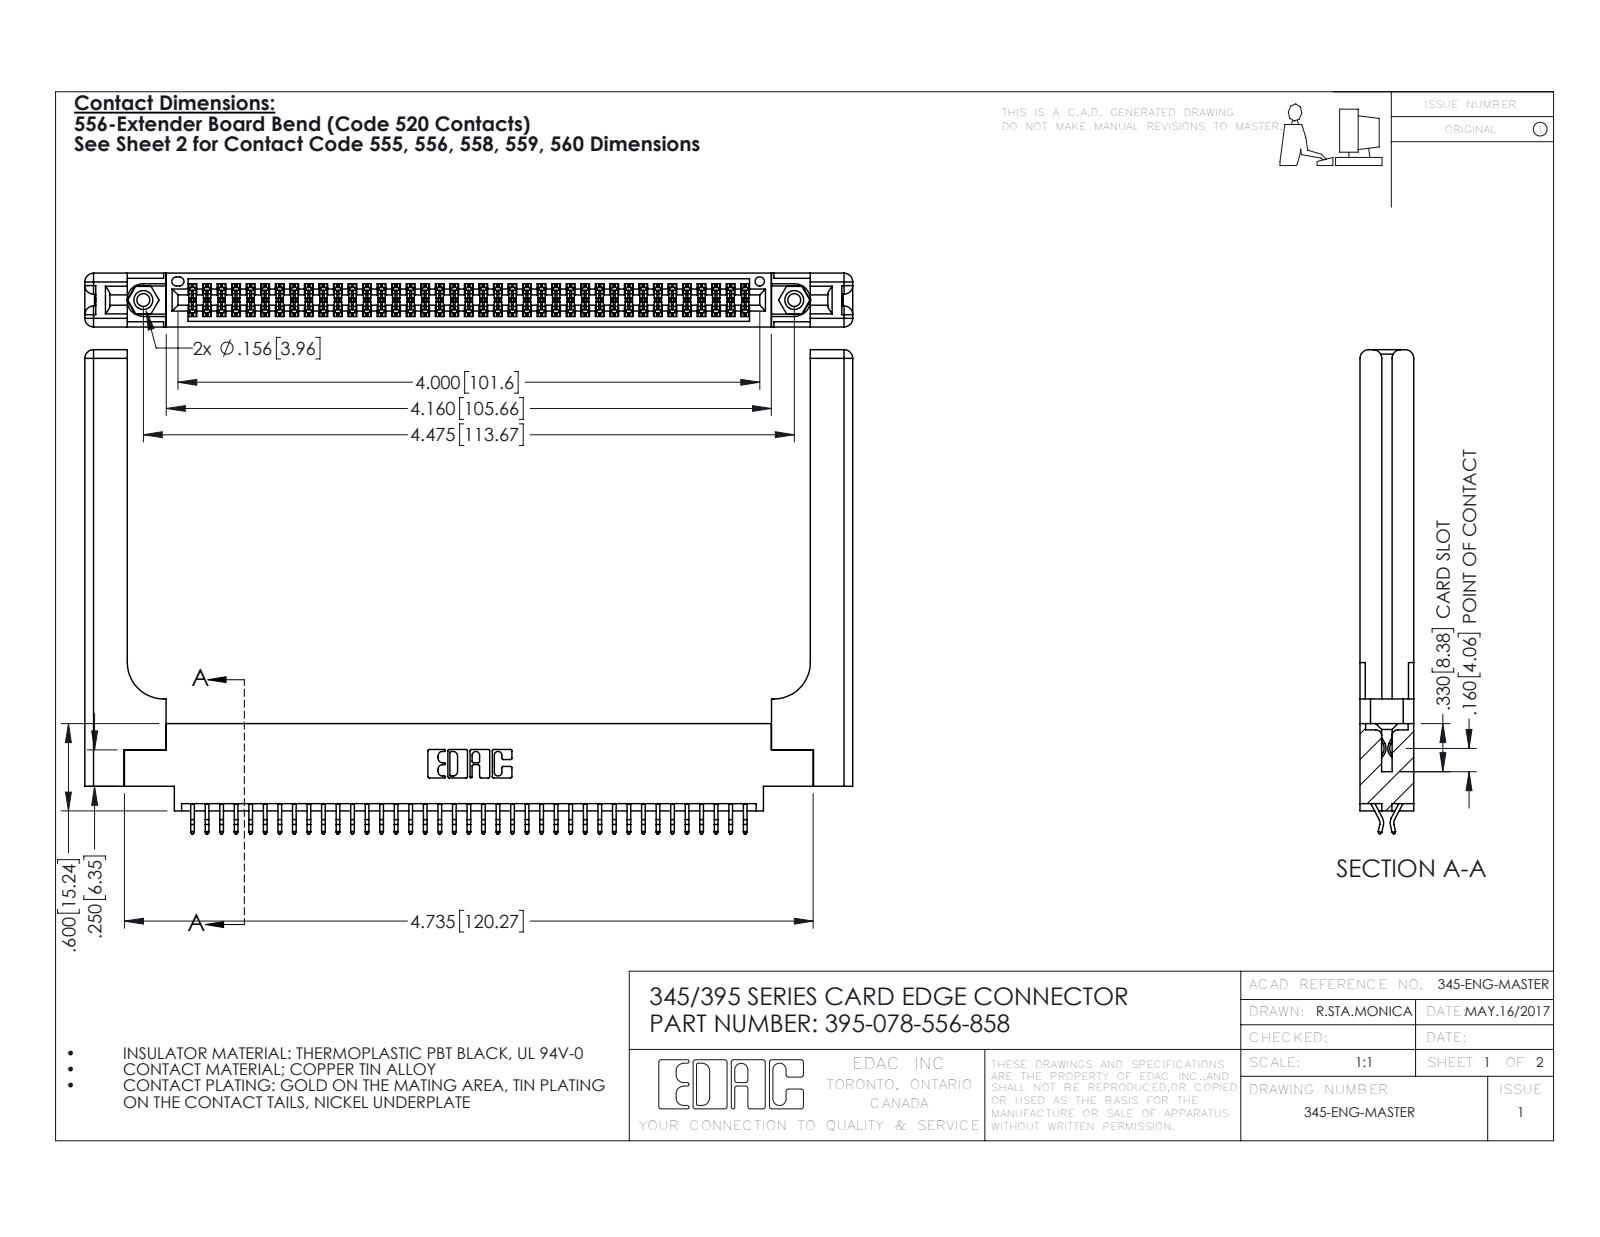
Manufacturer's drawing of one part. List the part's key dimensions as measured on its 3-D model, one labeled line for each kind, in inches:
Part name (STEP PRODUCT): 395-078-556-858; 345 Part_0.170 Offset - 0.156 Dia-TH; 345-220-058_345-220-058; 345-250-001_345-250-001-102 (+1 more)
STEP written by: SolidWorks 2016 (CONFIG_CONTROL_DESIGN)
Units: inches
Bodies: 83 solids, 4754 faces (3118 planar, 1576 cylindrical, 60 other)
Overall size (bounding box): 5.279 × 3.327 × 0.37
Volume: 1.303 in³ · Surface area: 37.38 in²
Round holes (diameter × count): ⌀0.089 ×2, ⌀0.125 ×2, ⌀0.156 ×2, ⌀0.064 ×1
Round bosses / shafts (diameter × count): ⌀0.155 ×2
Partial cylindrical surfaces — rounded edges, fillets, slot ends (radius × count): R0.006 ×117, R0.01 ×22, R0.06 ×16, R0.007 ×6, R0.031 ×6, R0.026 ×3, R0.01 ×2, R0.014 ×2
Main face-to-face distances: 0.37, 0.072, 0.298, 0.025, 0.098, 0.272, 0.2, 0.225, 0.148, 0.15
Hole centre spacings: 0.27, 4.239, 4.475
